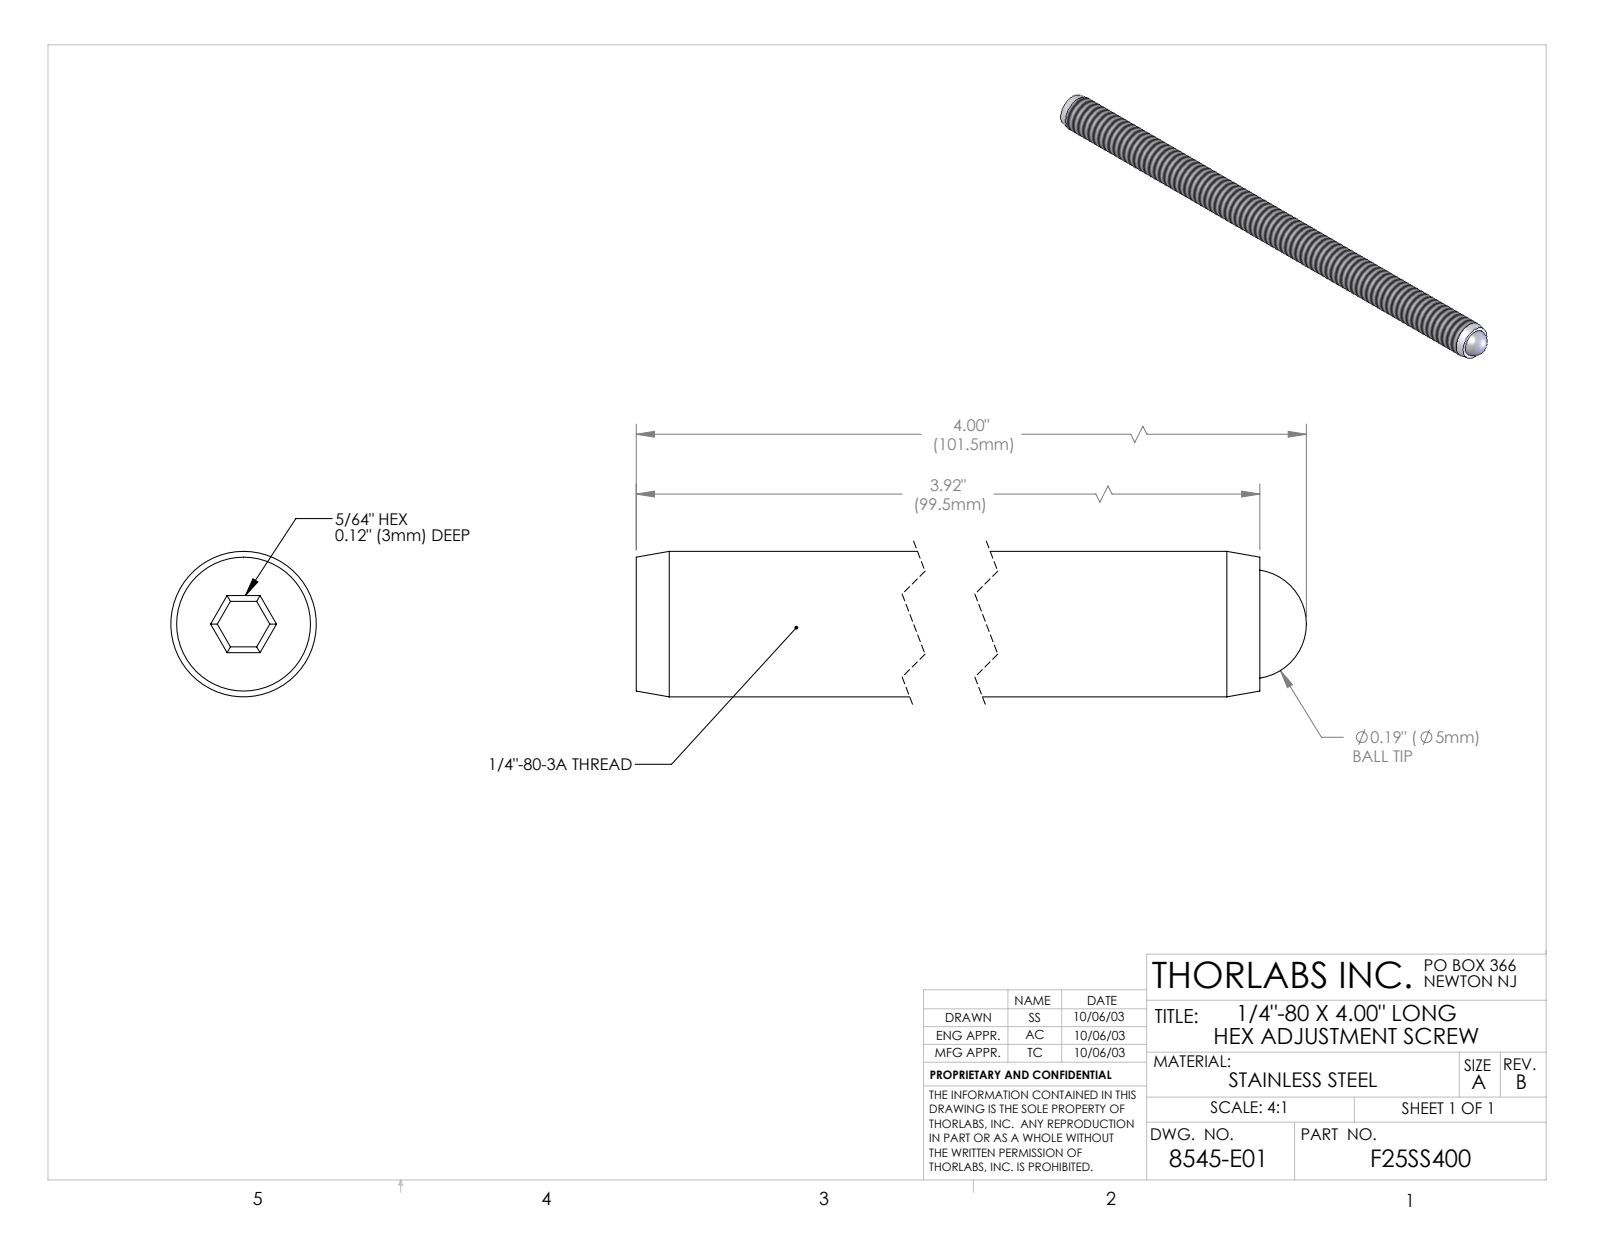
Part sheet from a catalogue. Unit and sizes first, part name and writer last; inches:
Units: inches
Overall size (bounding box): 4 × 0.25 × 0.25
Round holes (diameter × count): ⌀0.188 ×1
Round bosses / shafts (diameter × count): ⌀0.25 ×1
Main face-to-face distances: 3.92, 0.078, 0.12, 3.8, 0.078
Volume: 0.192 in³ · Surface area: 3.343 in²
Bodies: 2 solids, 29 faces (15 planar, 4 cylindrical, 10 other)
Part name (STEP PRODUCT): 8545-E0W
STEP written by: SolidWorks 2007 (AUTOMOTIVE_DESIGN)
